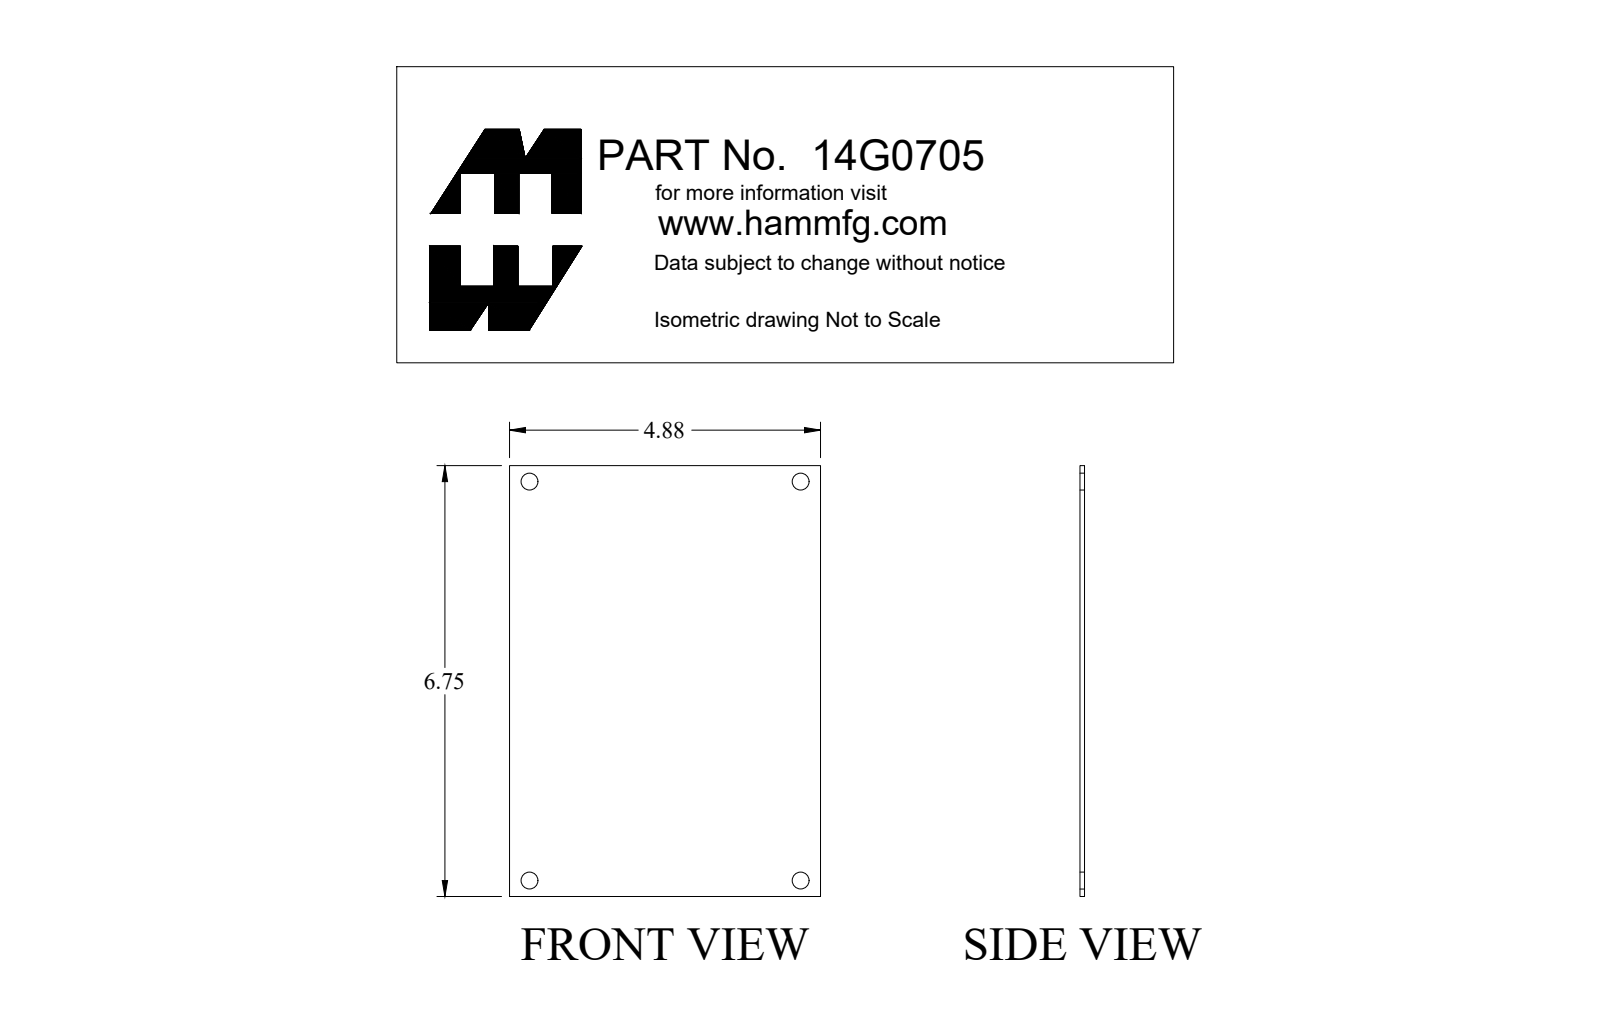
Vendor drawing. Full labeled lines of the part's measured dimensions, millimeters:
Part name (STEP PRODUCT): 14G0705
STEP written by: SolidWorks 2018 (AUTOMOTIVE_DESIGN)
Units: millimetres
Bodies: 1 solid, 10 faces (6 planar, 4 cylindrical, 0 other)
Overall size (bounding box): 171.5 × 123.8 × 1.8
Volume: 38 560 mm³ · Surface area: 43 410 mm²
Round holes (diameter × count): ⌀6.7 ×4
Main face-to-face distances: 1.8, 123.8, 171.5
Hole centre spacings: 108, 158.8, 192
